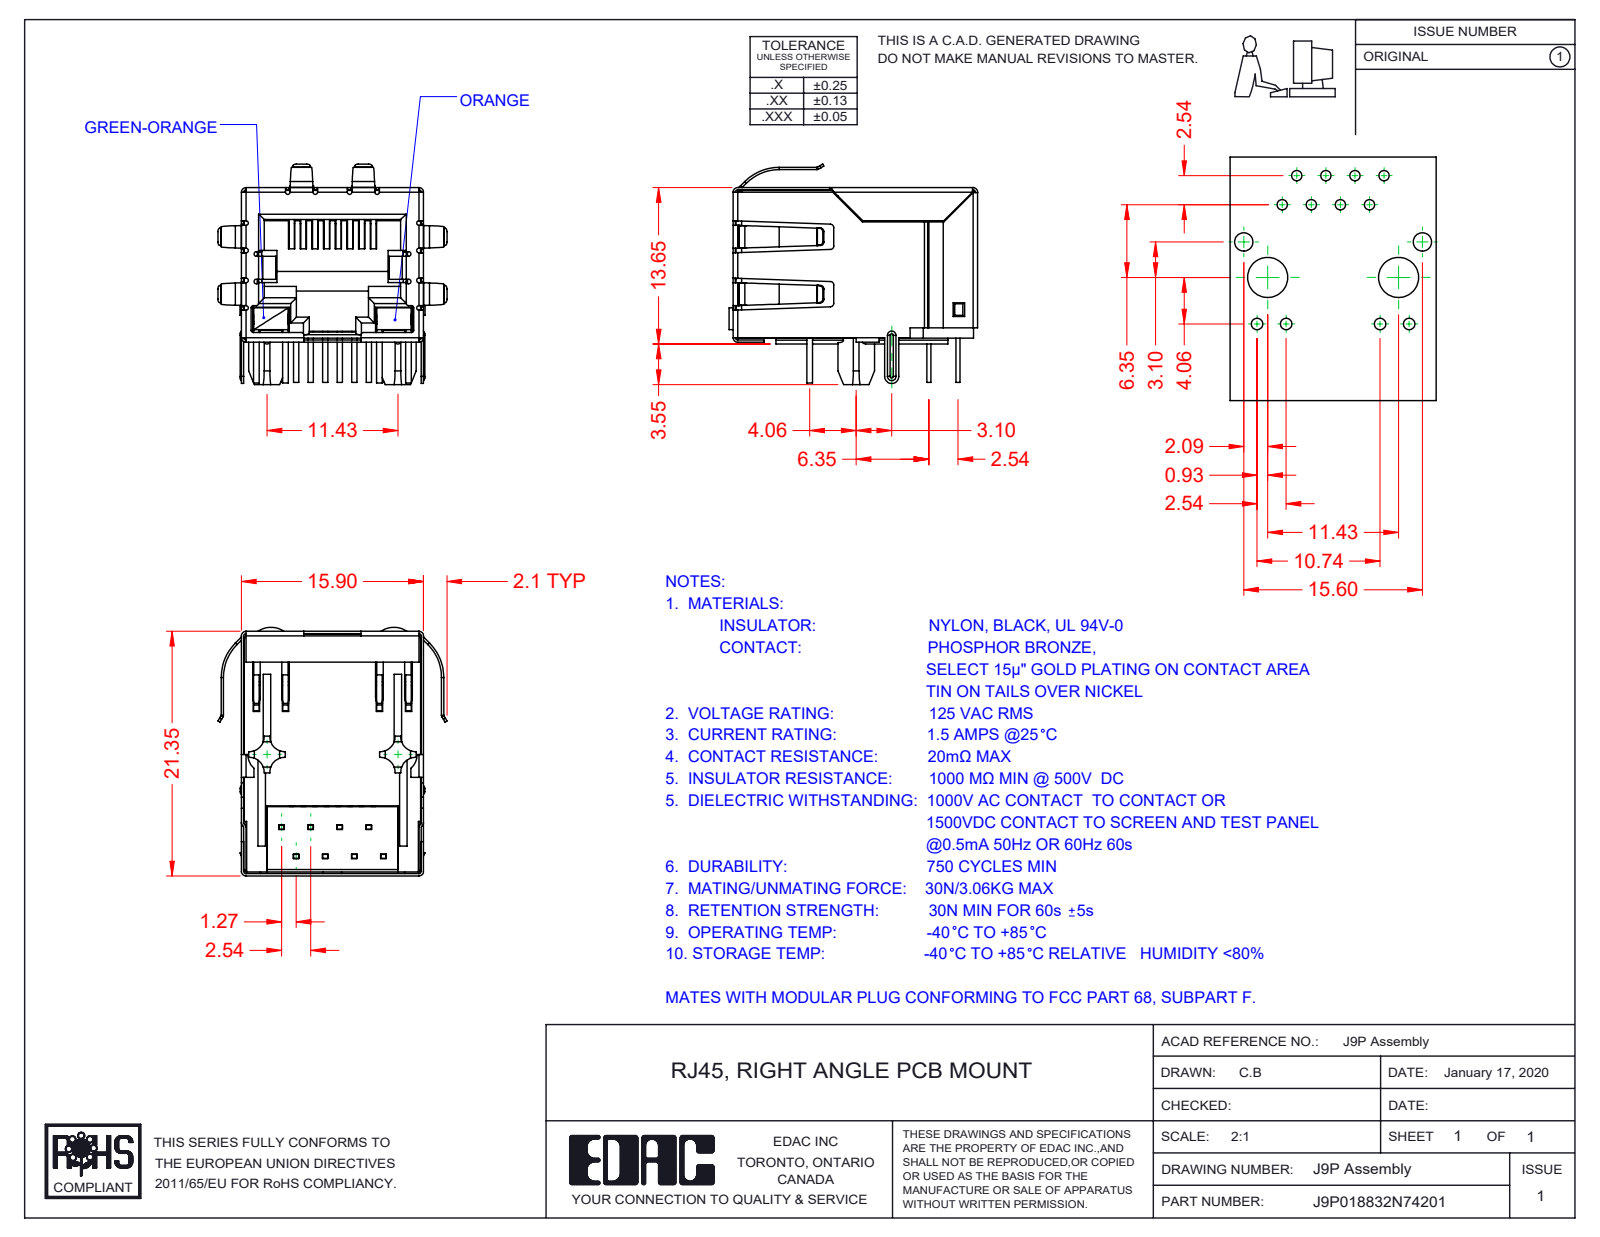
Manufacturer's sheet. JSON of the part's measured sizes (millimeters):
{"part_name": "9P-LED Contact Lock; 9P-LED LED LH_7-Green-Orange; 9P-LED Shield; 9P-LED Assembly (+4 more)", "step_written_by": "SolidWorks 2016 (CONFIG_CONTROL_DESIGN)", "units": "millimeters", "bodies": {"solids": 13, "faces": 1474, "planar": 1042, "cylindrical": 338, "other": 94}, "overall_size": [21.7, 20, 19.25], "volume_mm3": 2687, "surface_area_mm2": 7515, "partial_cylinders_radius": [[0.2, 39], [0.5, 22], [0.3, 20], [0.4, 16], [1.3, 8], [0.23, 5], [0.11, 4], [0.31, 4]], "face_to_face_distances": [15.45, 15.7, 15.65, 0.35, 0.54, 15.5, 12.36, 0.6, 1.4, 0.59]}
